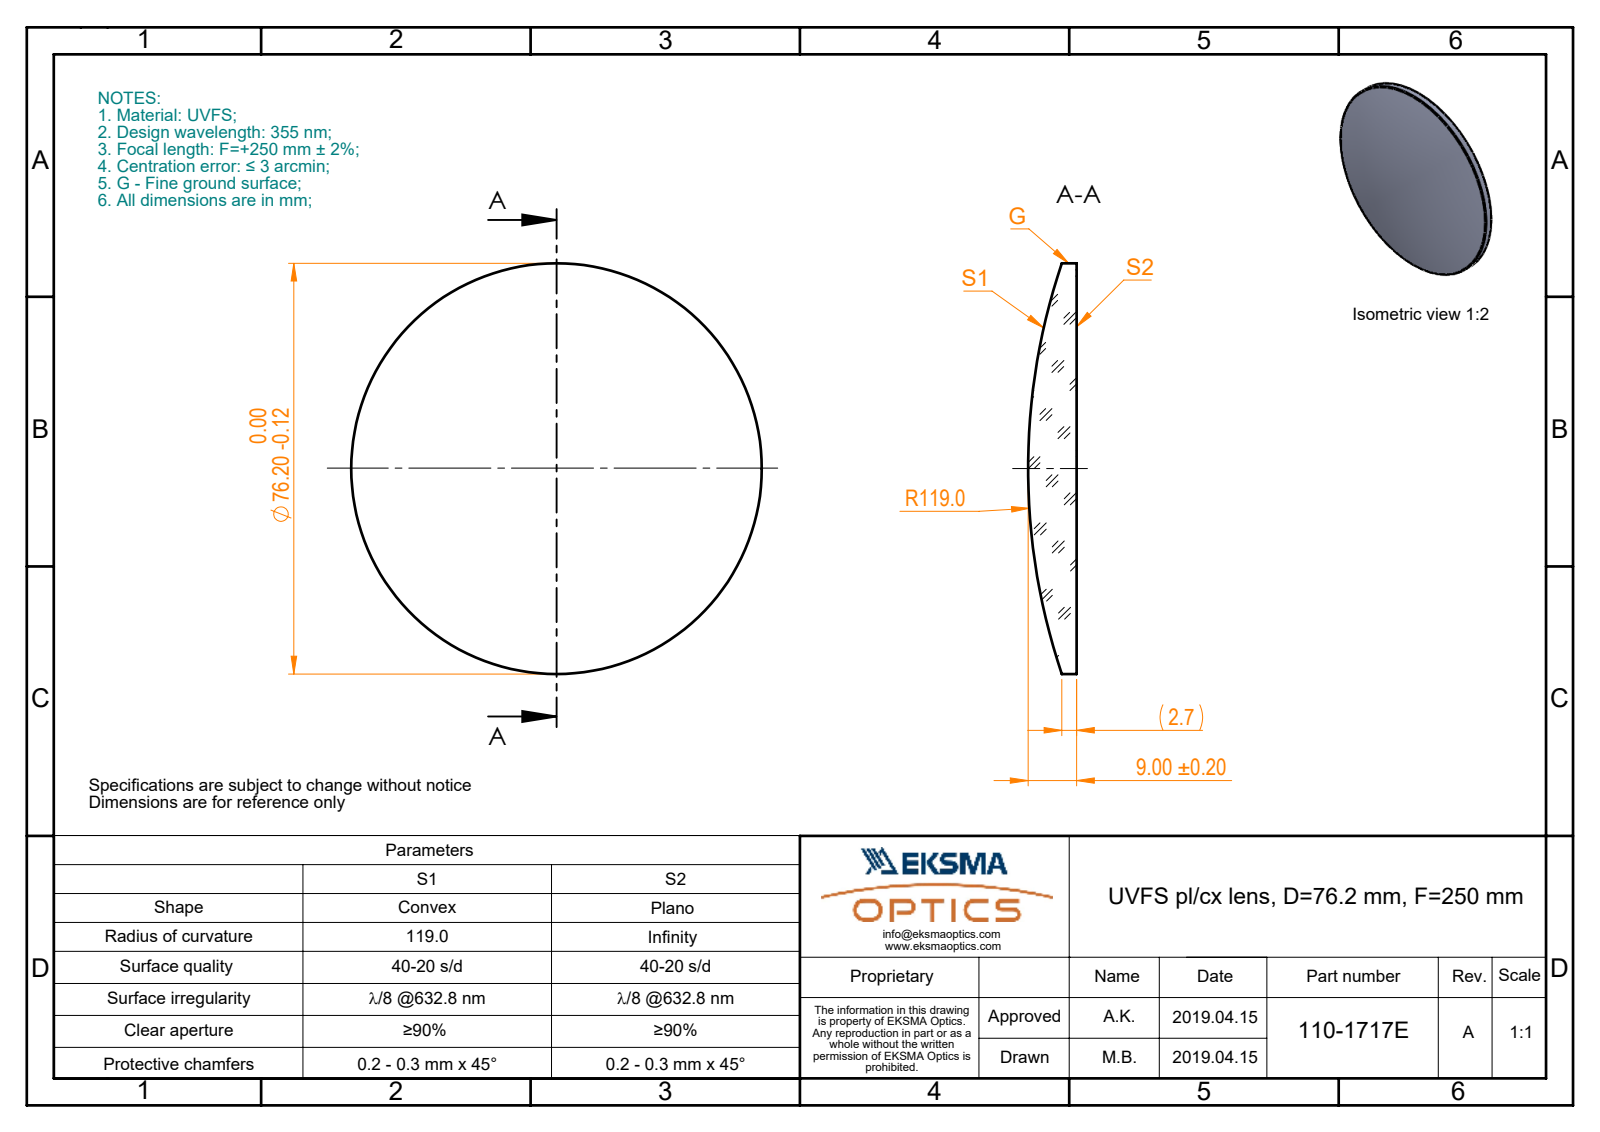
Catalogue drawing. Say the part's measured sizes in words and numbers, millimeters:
The part is named "110-1717E UVFS pl-cx 76.2 F250". Its 3-D file was written by "SolidWorks 2017 (CONFIG_CONTROL_DESIGN)". It is 1 solid with 5 faces: 1 planar, 2 cylindrical and 2 other. Overall it measures 76.2 by 76.2 by 9 millimeters. Its volume is 26 889 cubic millimeters and its surface area 9 899 square millimeters. Round bosses or shafts: 1 of diameter 76.2.
